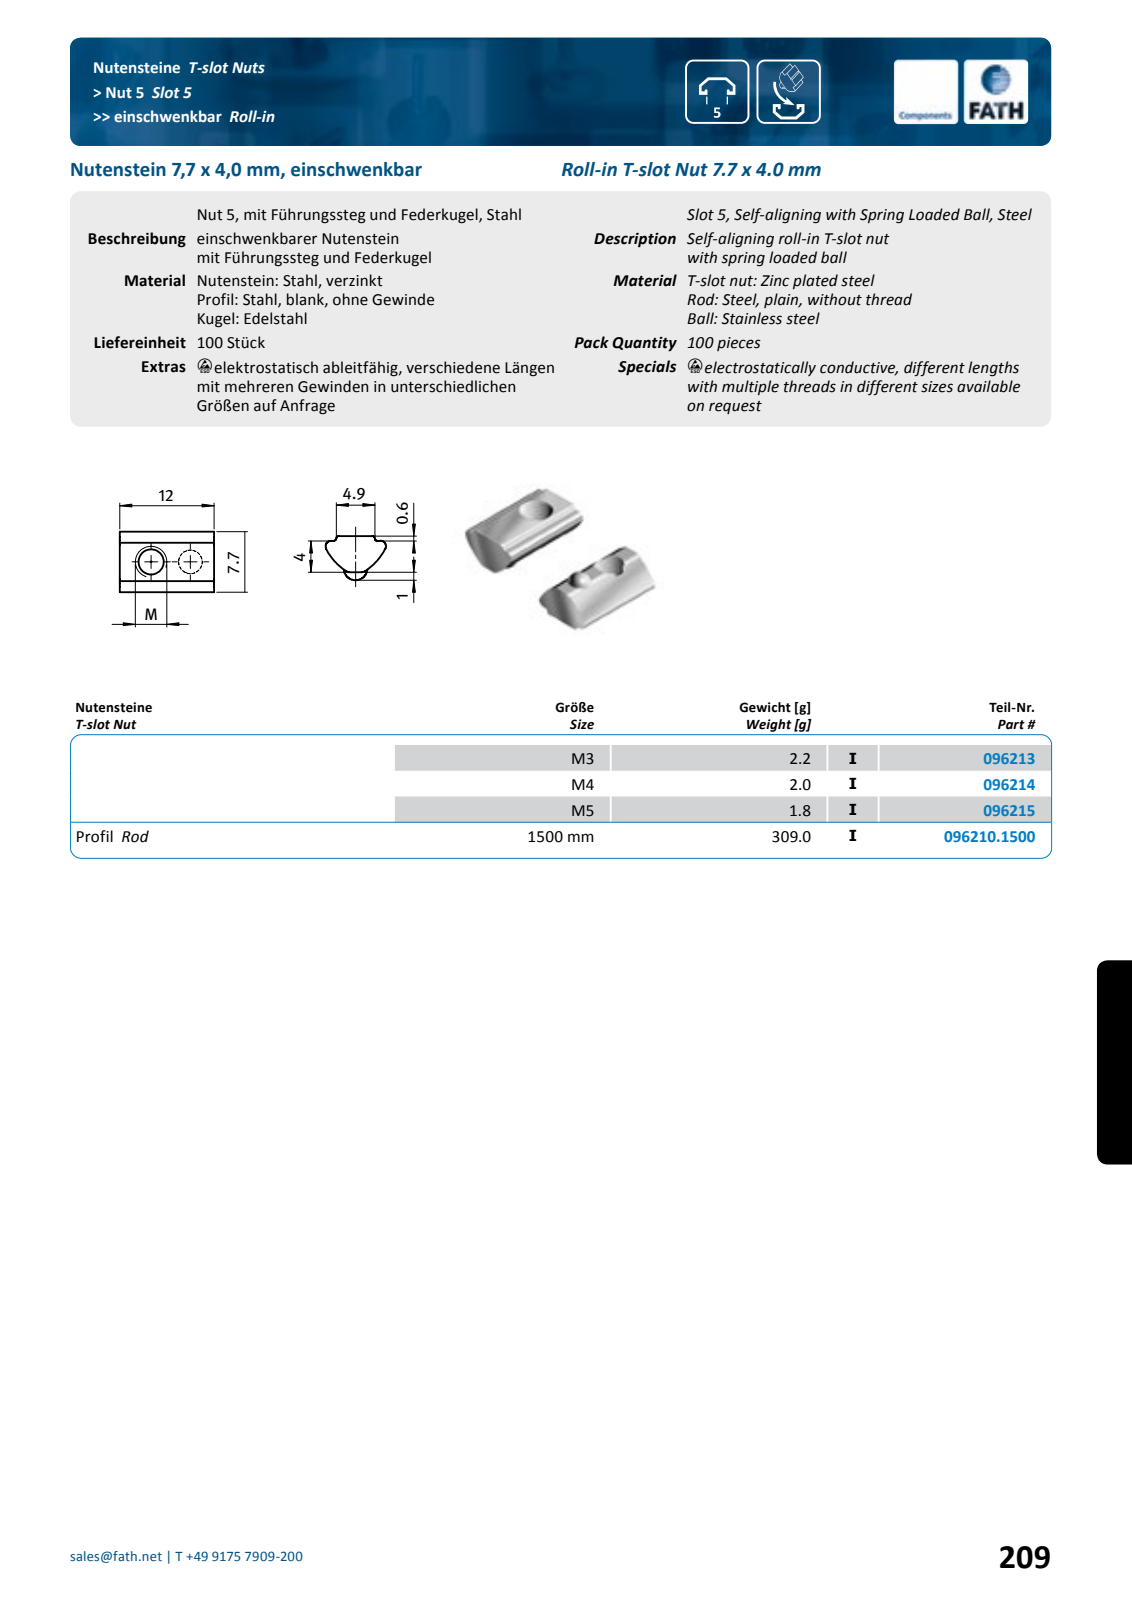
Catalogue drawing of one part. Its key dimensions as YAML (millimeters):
part_name: "fath_096213"
step_written_by: "Spatial InterOp 3D (automotive_design)"
units: millimeters
bodies: {solids: 1, faces: 39, planar: 9, cylindrical: 20, other: 10}
overall_size: [12, 7.7, 4.6]
volume: 265
surface_area: 354
round_holes:
  - {diameter: 2.4, count: 1}
  - {diameter: 3, count: 1}
partial_cylinders:
  - {radius: 0.3, count: 4}
  - {radius: 0.7, count: 4}
  - {radius: 7.5, count: 2}
face_to_face_distances: [12, 4.6, 4, 0.6, 4.5, 0.5]
hole_center_spacings: [6]
